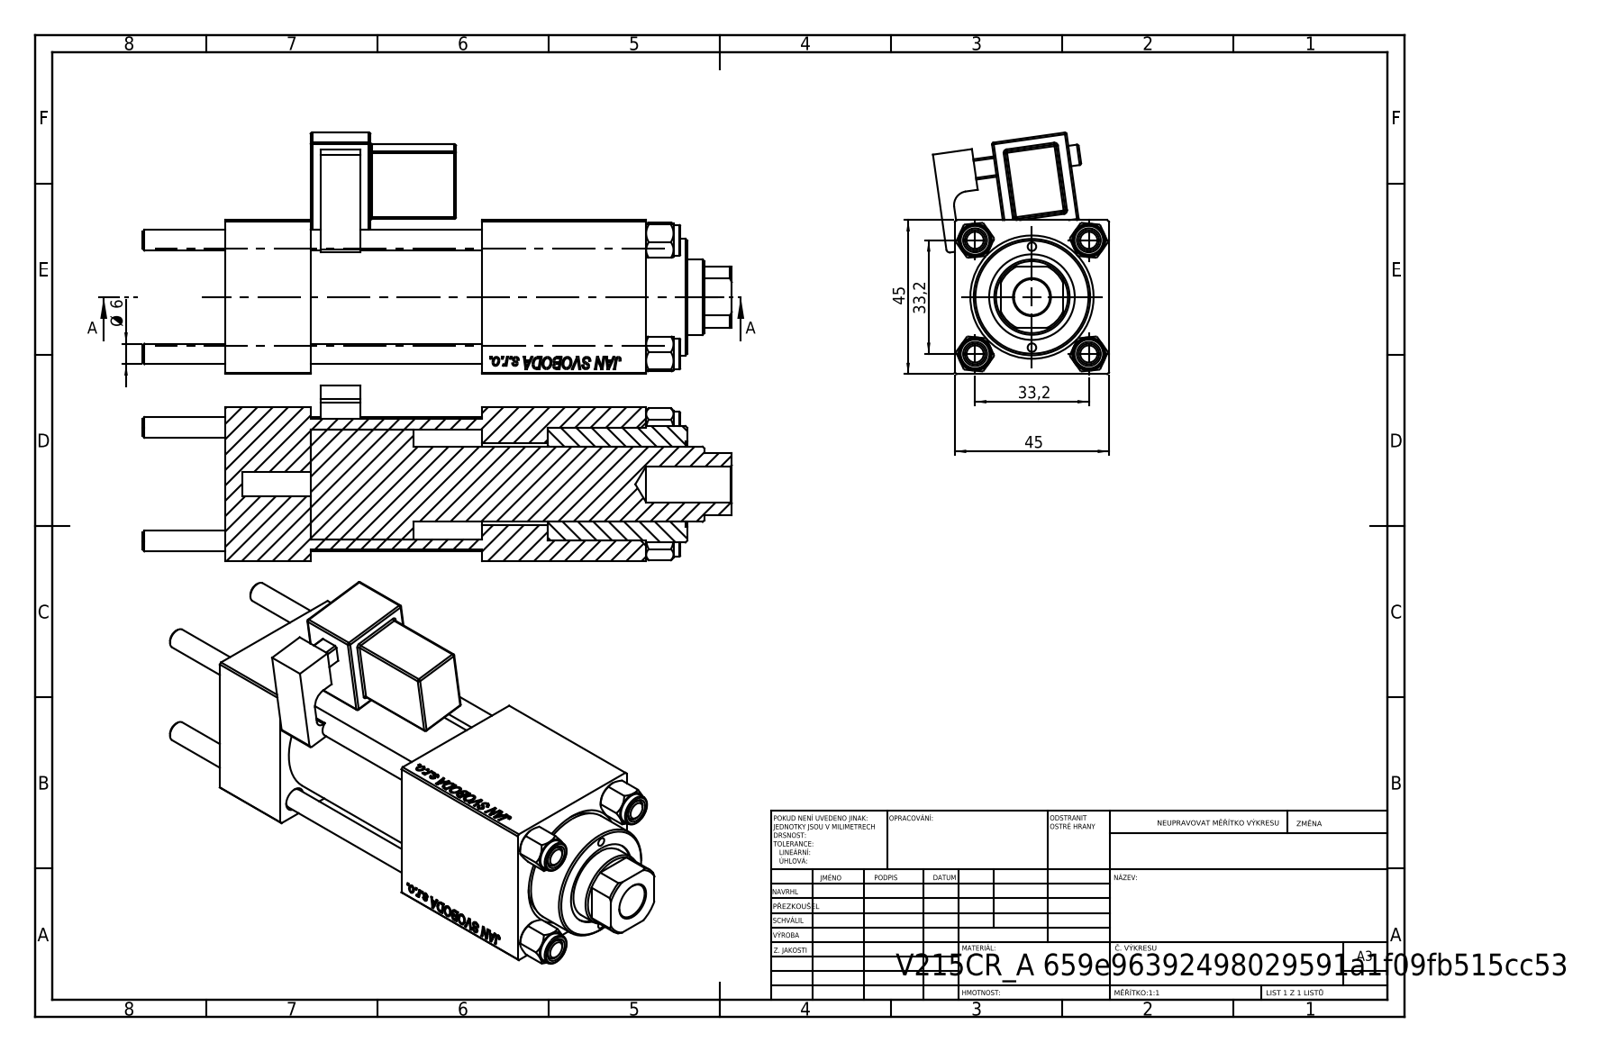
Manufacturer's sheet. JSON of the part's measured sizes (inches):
{"part_name": "V215_VC_A; NUT_M5; V215CR_MSU; CR025_012_A_0_G_A_G_M_020_+#_##_TYCINKA (+2 more)", "step_written_by": "SolidWorks 2019 (CONFIG_CONTROL_DESIGN)", "units": "inches", "bodies": {"solids": 12, "faces": 1218, "planar": 552, "cylindrical": 112, "other": 554}, "overall_size": [6.772, 2.779, 2.024], "volume_in3": 14.31, "surface_area_in2": 129.1, "round_holes": [[0.236, 4], [0.098, 2], [0.276, 2], [0.518, 2], [0.787, 2], [0.413, 1], [0.866, 1], [0.945, 1], [0.984, 1], [1.26, 1], [1.299, 1]], "round_bosses_or_shafts": [[0.354, 4], [1.496, 1], [1.339, 1], [0.236, 1]], "partial_cylinders_radius": [[0.02, 24], [0.039, 1], [0.098, 1], [0.157, 1], [0.413, 1]], "face_to_face_distances": [1.772, 0.984, 4.843, 1.969, 2.953, 3.858, 1.89, 3.713, 2.728, 0.76], "hole_center_spacings": [0.657, 0.924, 1.307, 1.396, 0.581, 1.848, 1.161, 2.972]}
